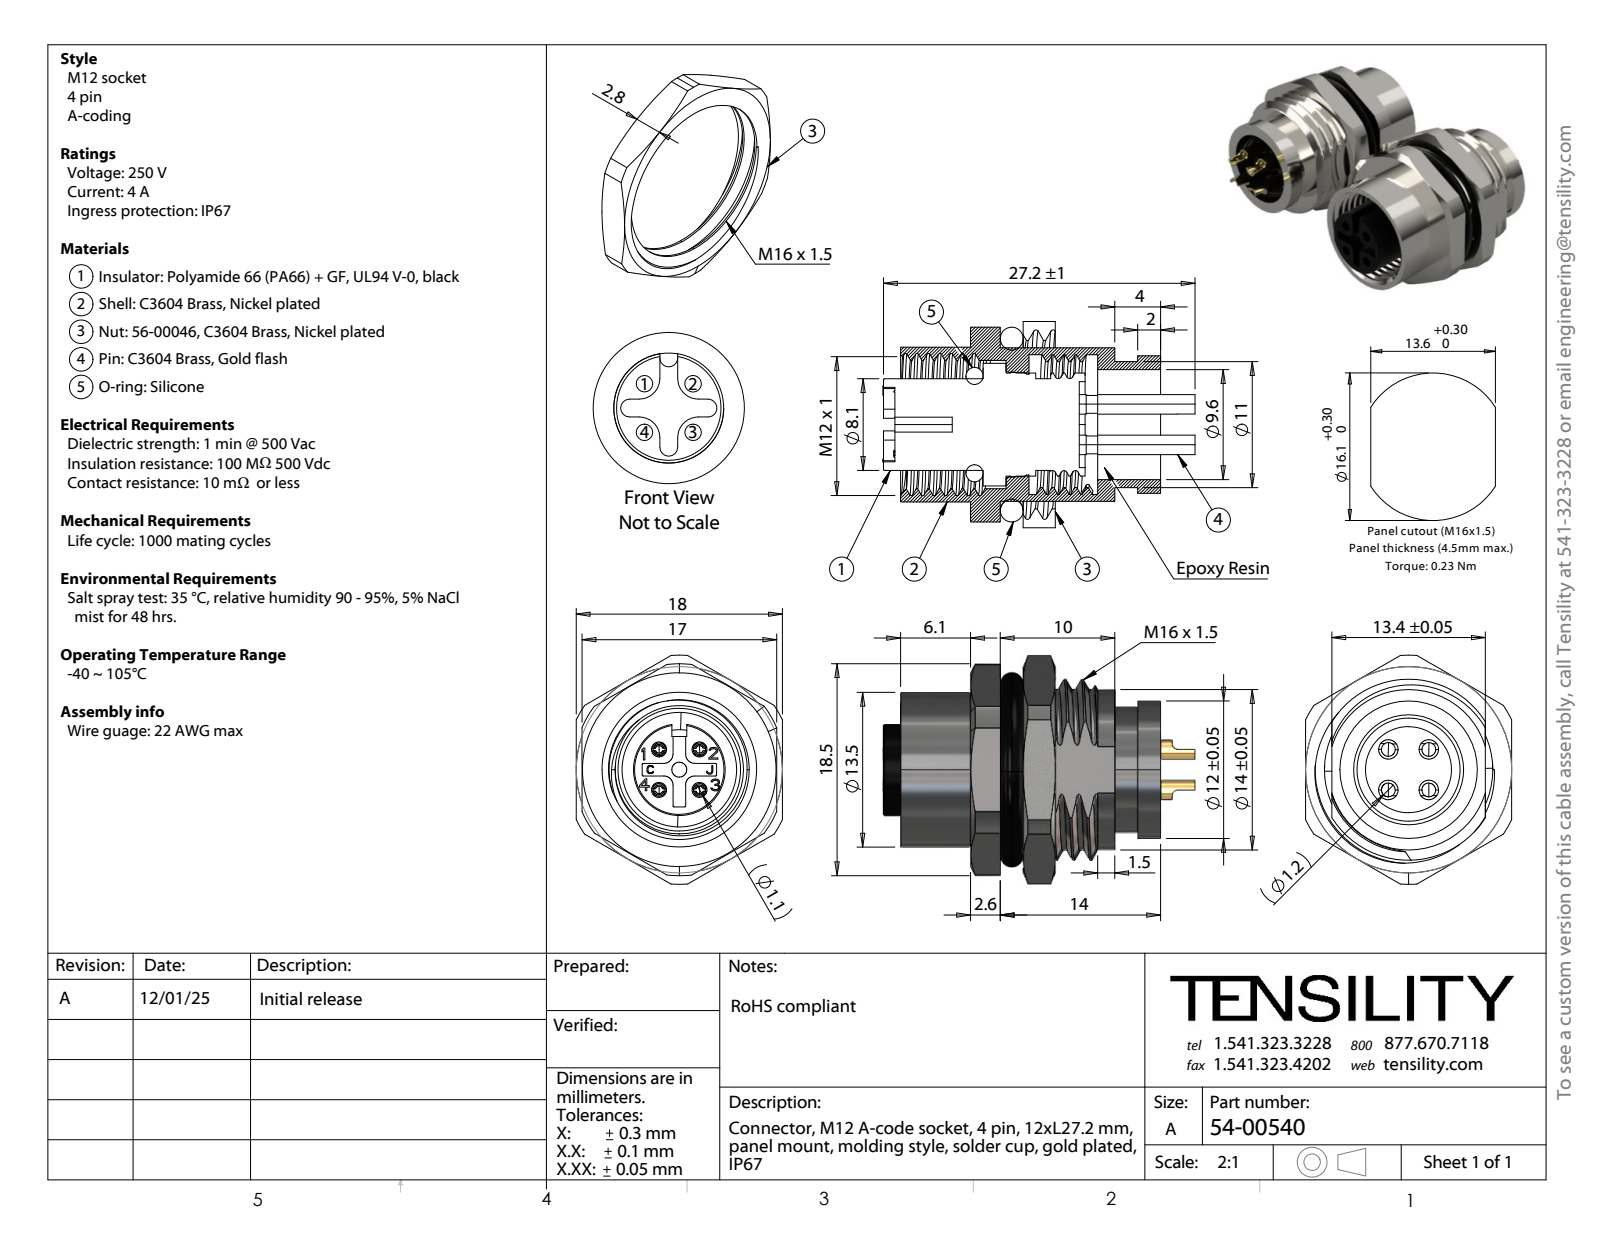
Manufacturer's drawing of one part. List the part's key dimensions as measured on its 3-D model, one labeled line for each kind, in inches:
Part name (STEP PRODUCT): 54-00540; 56-00046
STEP written by: SolidWorks 2025 (CONFIG_CONTROL_DESIGN)
Units: inches
Bodies: 9 solids, 694 faces (308 planar, 210 cylindrical, 176 other)
Overall size (bounding box): 1.073 × 0.787 × 0.709
Volume: 0.171 in³ · Surface area: 8.382 in²
Round holes (diameter × count): ⌀0.051 ×5, ⌀0.047 ×4, ⌀0.063 ×4, ⌀0.295 ×1, ⌀0.346 ×1, ⌀0.358 ×1, ⌀0.378 ×1, ⌀0.441 ×1, ⌀0.48 ×1, ⌀0.579 ×1
Round bosses / shafts (diameter × count): ⌀0.067 ×4, ⌀0.061 ×4, ⌀0.06 ×4, ⌀0.551 ×1, ⌀0.549 ×1, ⌀0.531 ×1, ⌀0.472 ×1, ⌀0.433 ×1
Partial cylindrical surfaces — rounded edges, fillets, slot ends (radius × count): R0.004 ×6, R0.031 ×4, R0.02 ×3, R0.311 ×1, R0.364 ×1, R0.394 ×1
Main face-to-face distances: 0.02, 0.079, 0.059, 0.394, 0.102, 0.374, 0.689, 0.122, 0.315, 0.091
Hole centre spacings: 0.098, 0.139, 0.139, 0.197
